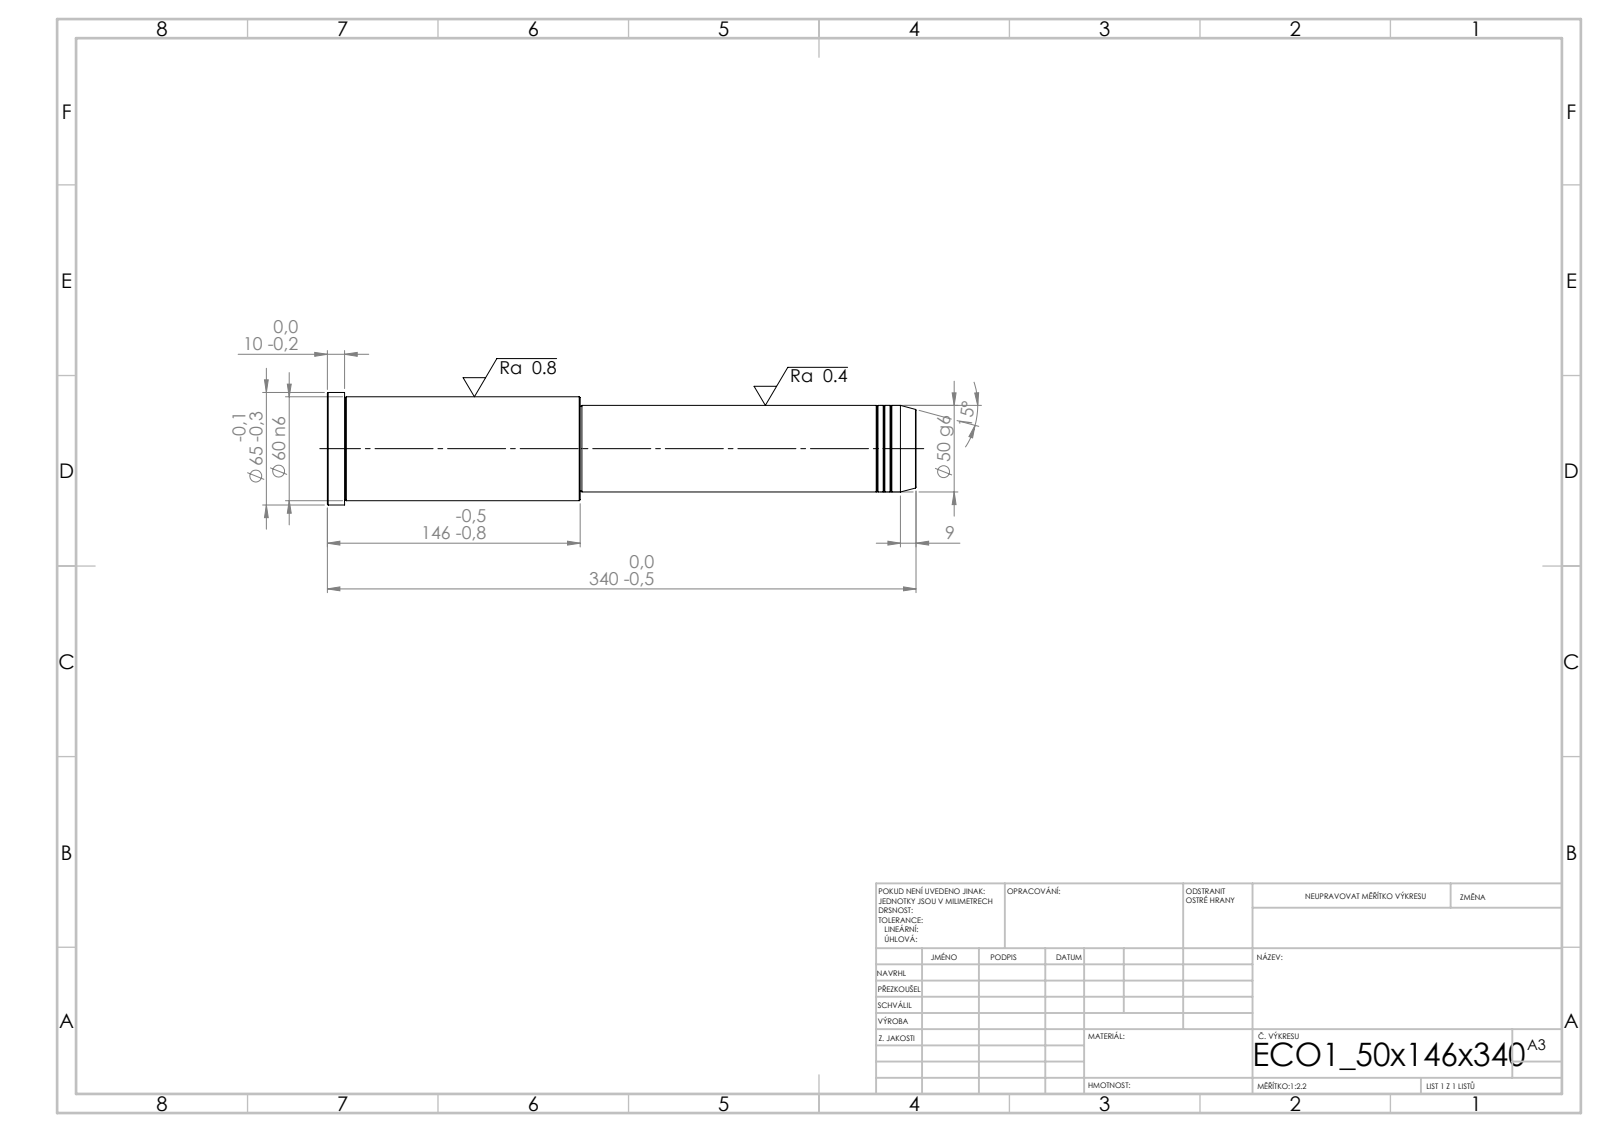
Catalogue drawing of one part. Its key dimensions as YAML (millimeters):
step_written_by: "SolidWorks 2019 (CONFIG_CONTROL_DESIGN)"
units: millimeters
bodies: {solids: 1, faces: 43, planar: 5, cylindrical: 14, other: 24}
overall_size: [340, 65, 65]
volume: 796595
surface_area: 64791
round_bosses_or_shafts:
  - {diameter: 65, count: 1}
  - {diameter: 60, count: 1}
  - {diameter: 50, count: 1}
  - {diameter: 49, count: 1}
face_to_face_distances: [340, 194, 146, 330, 136, 10, 193, 1, 137, 147]
